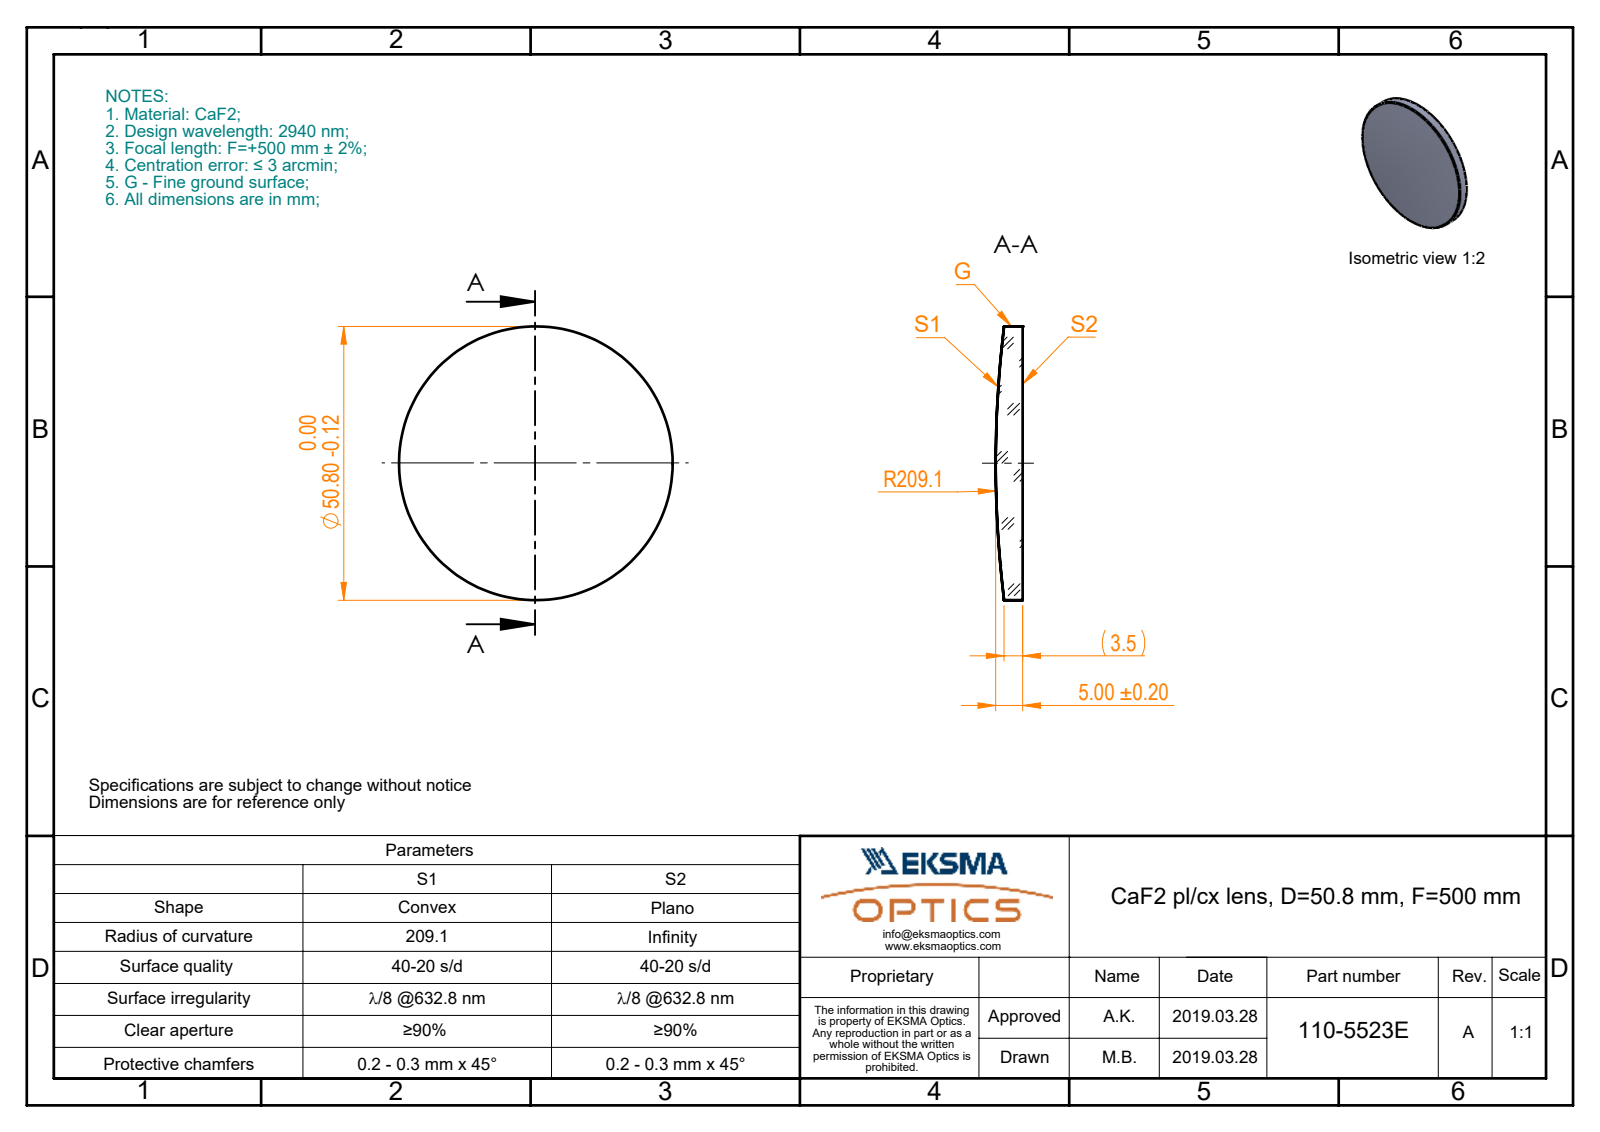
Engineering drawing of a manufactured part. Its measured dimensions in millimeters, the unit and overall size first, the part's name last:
Units: millimetres
Overall size (bounding box): 50.8 × 50.8 × 5
Round bosses / shafts (diameter × count): ⌀50.8 ×1
Volume: 8 567 mm³ · Surface area: 4 612 mm²
Bodies: 1 solid, 5 faces (1 planar, 2 cylindrical, 2 other)
Part name (STEP PRODUCT): 110-5523E CaF2 pl-cx 50.8 F500
STEP written by: SolidWorks 2017 (CONFIG_CONTROL_DESIGN)
